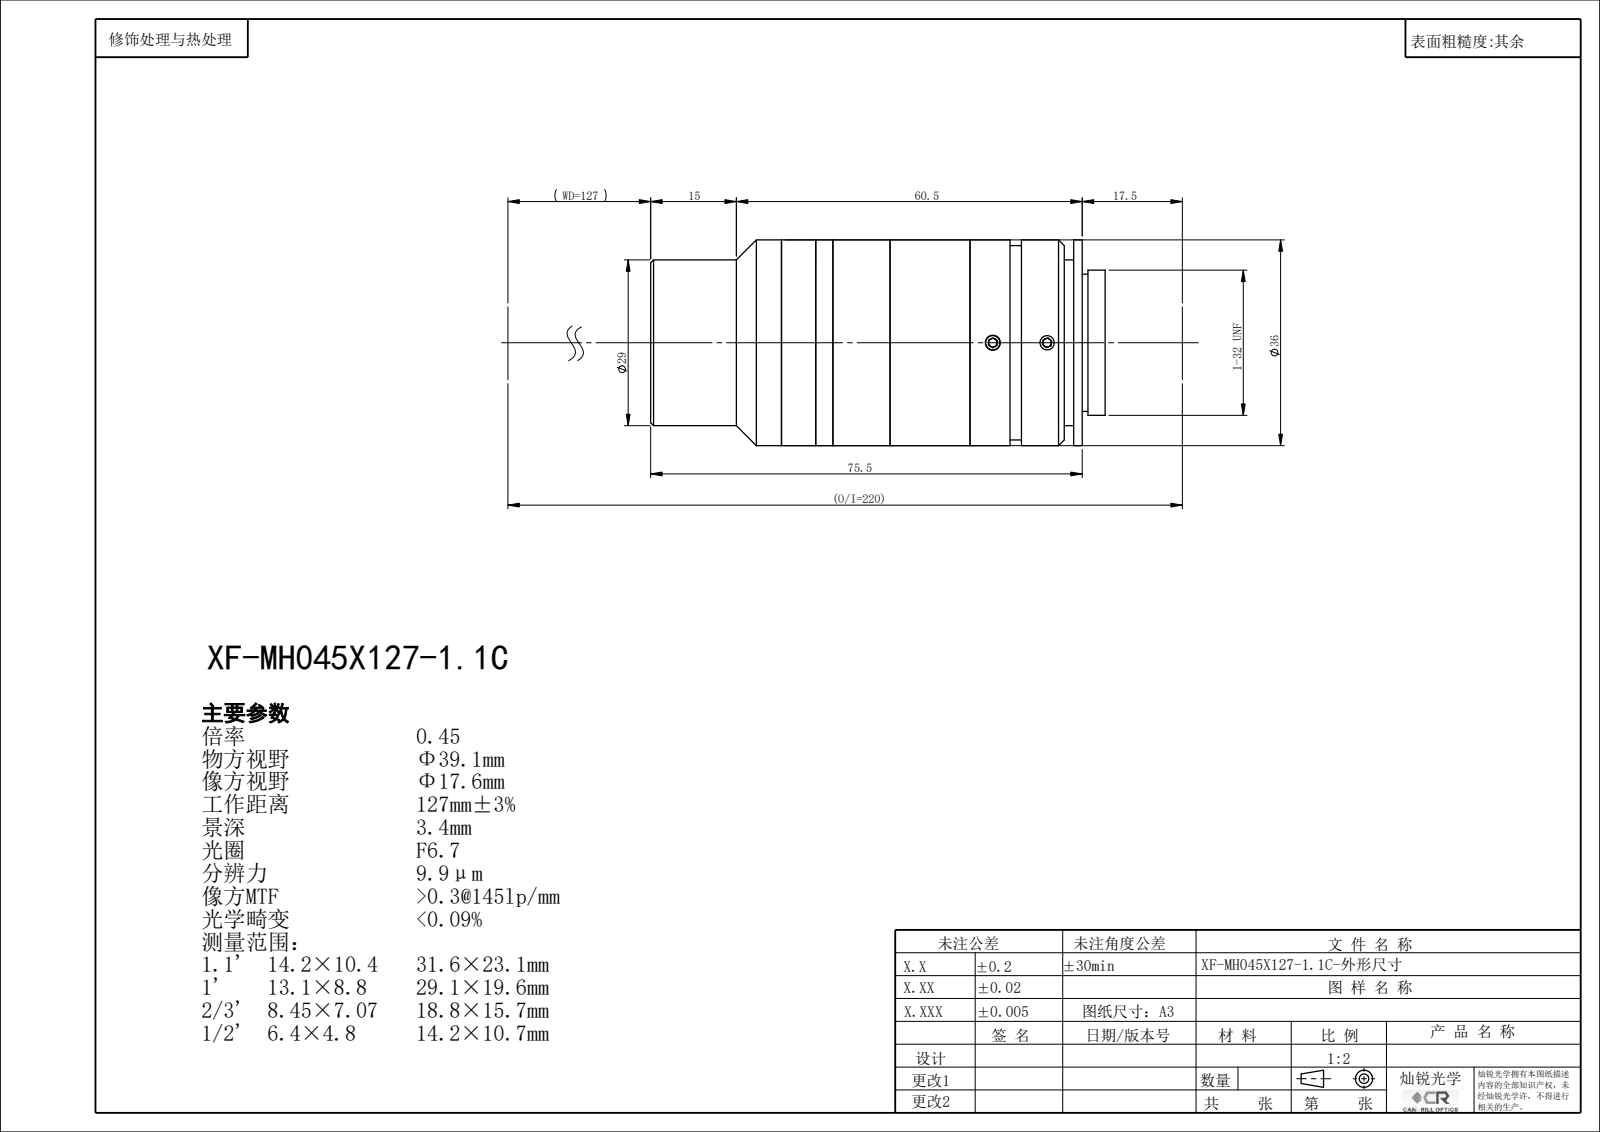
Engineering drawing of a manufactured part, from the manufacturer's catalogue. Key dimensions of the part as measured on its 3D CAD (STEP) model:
Part name (STEP PRODUCT): XF-MH045X127-1.1C
STEP written by: SolidWorks 2022 (CONFIG_CONTROL_DESIGN)
Units: millimetres
Bodies: 0 solids, 143 faces (70 planar, 44 cylindrical, 29 other)
Overall size (bounding box): 79.55 × 36 × 36
Round holes (diameter × count): ⌀2.5 ×3, ⌀20 ×1, ⌀22.4 ×1, ⌀24 ×1, ⌀24.9 ×1, ⌀26 ×1, ⌀26.4 ×1
Round bosses / shafts (diameter × count): ⌀36 ×1, ⌀34 ×1, ⌀29 ×1, ⌀25.4 ×1
Main face-to-face distances: 19.65, 1.5, 18.15, 14, 32.15, 33.65, 10, 24, 42.15, 43.65
